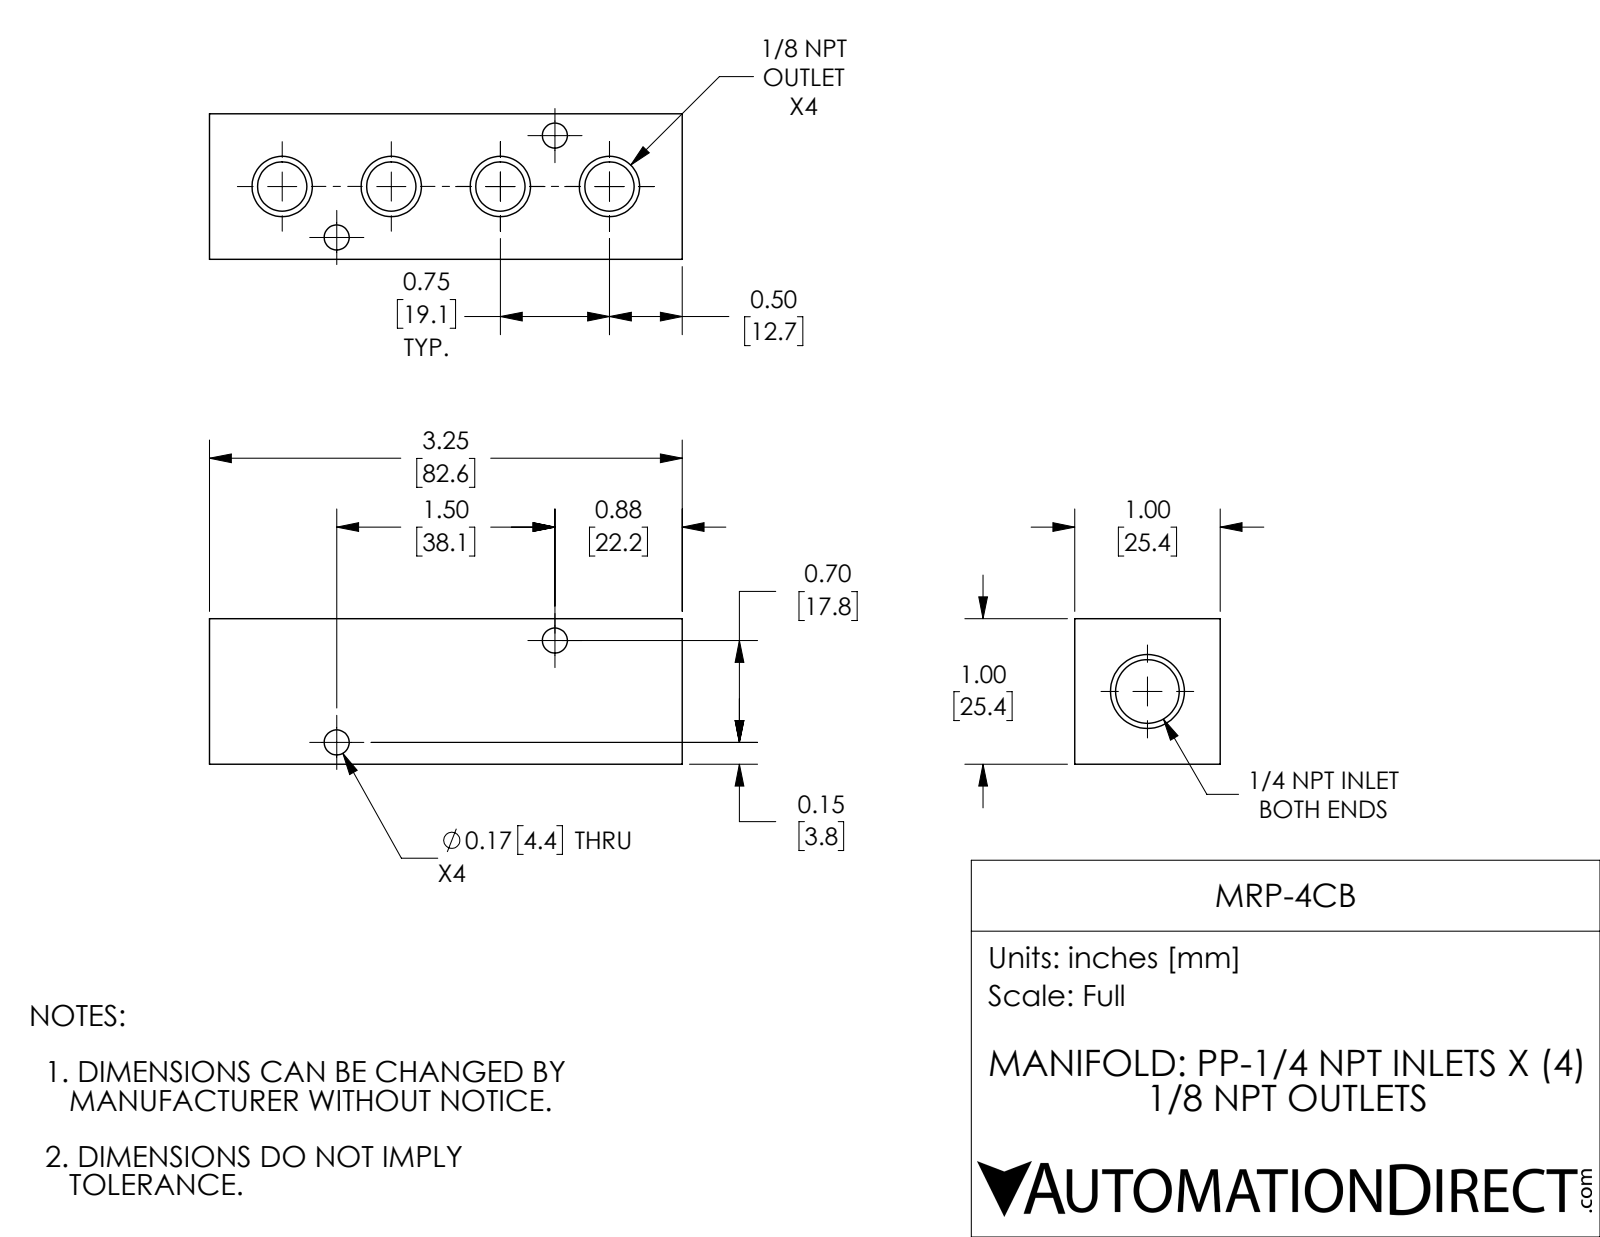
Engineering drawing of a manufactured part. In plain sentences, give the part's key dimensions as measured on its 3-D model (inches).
The part is named "MRP-4CB". Its 3-D file was written by "SolidWorks 2018 (AUTOMOTIVE_DESIGN)". It is 1 solid with 44 faces: 6 planar, 26 cylindrical and 12 other. Overall it measures 3.25 by 1 by 1 inches. Its volume is 2.561 cubic inches and its surface area 21.37 square inches. Round holes: 4 of diameter 0.172, 4 of diameter 0.339, 1 of diameter 0.438. The main face-to-face distances are 1, 3.25. The hole center spacings are 0.513, 0.75, 1.178, 1.5, 1.656, 1.907, 2.25.
